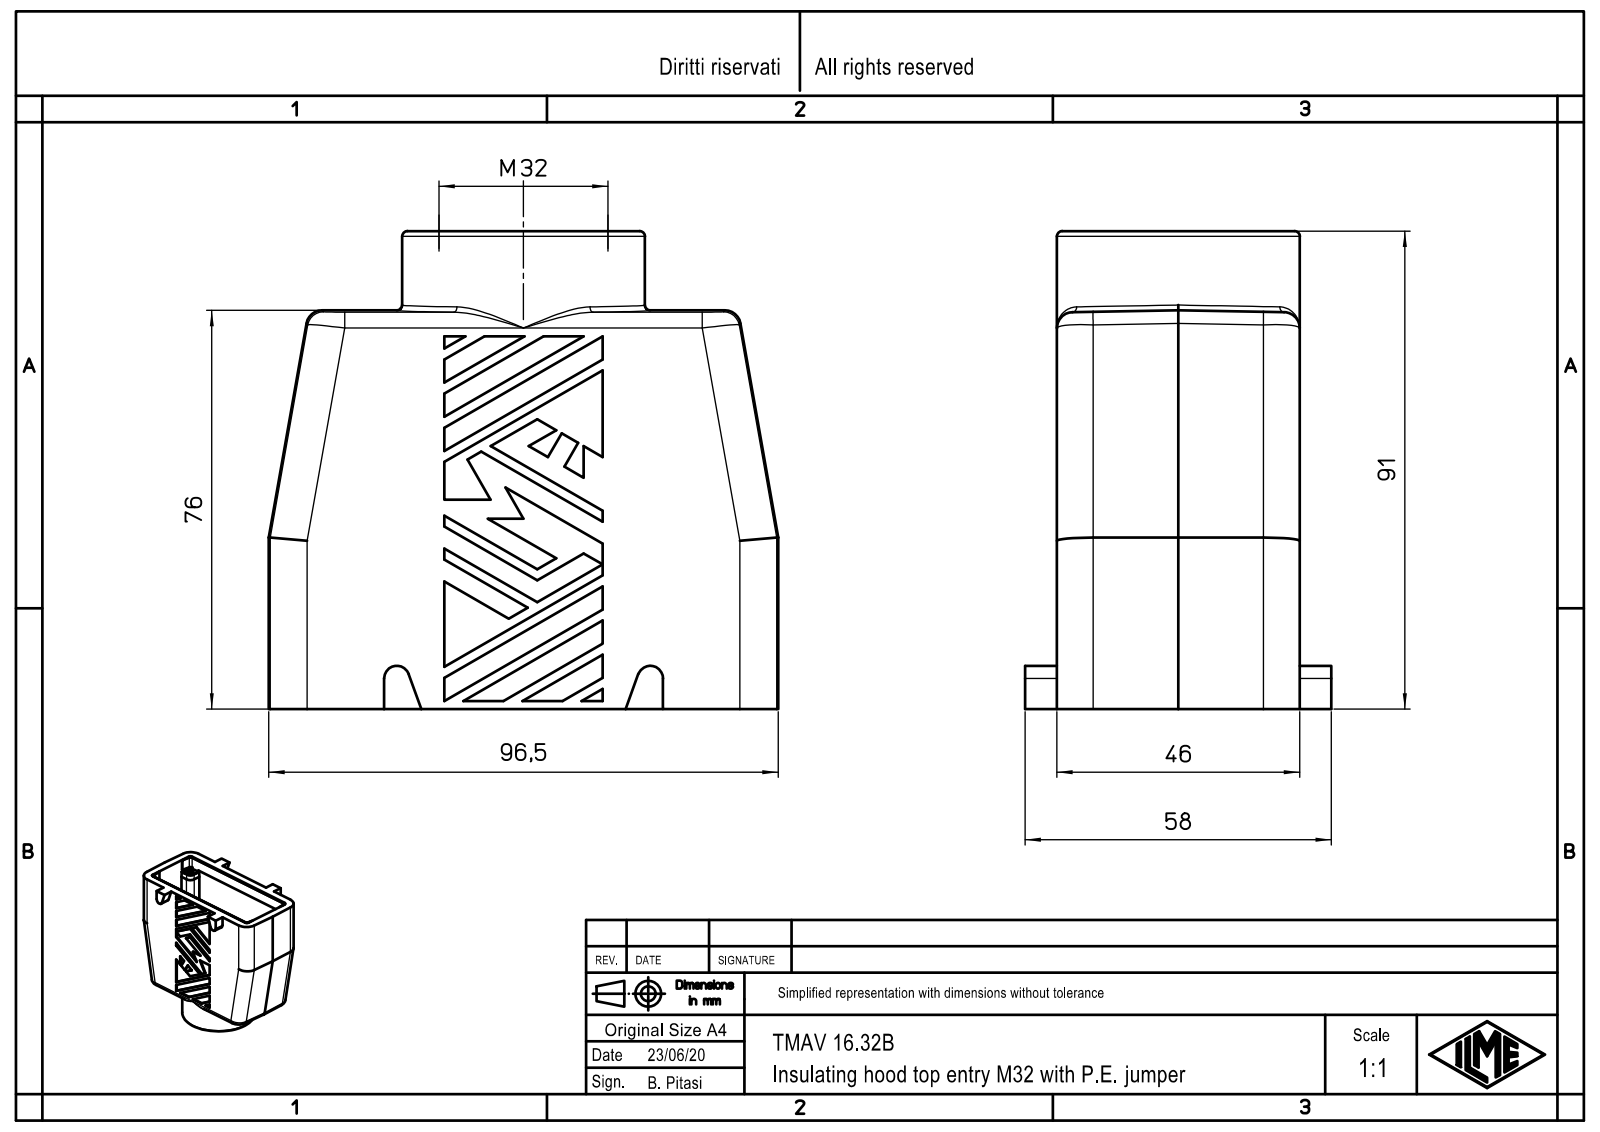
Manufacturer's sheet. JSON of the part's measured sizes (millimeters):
{"part_name": "TMAV_16.32B", "step_written_by": "Creo Elements/Direct Modeling 20.1B 02-Apr-2019 (C) Parametric Technology GmbH (AUTOMOTIVE_DESIGN)", "units": "millimeters", "bodies": {"solids": 1, "faces": 466, "planar": 302, "cylindrical": 82, "other": 82}, "overall_size": [96.5, 90.49, 58], "volume_mm3": 137745, "surface_area_mm2": 51504, "round_holes": [[3, 4], [3.5, 4], [28, 1], [32, 1]], "round_bosses_or_shafts": [[4.8, 4], [46, 1]], "partial_cylinders_radius": [[1.5, 12], [7, 8], [3, 6], [1.3, 4], [1.6, 4], [2, 4], [3.5, 4], [2.4, 2]], "face_to_face_distances": [46, 0.5, 45.5, 69.99, 5.6, 45, 5.3, 5.8, 40.2, 39.7], "hole_center_spacings": [41.03, 27, 77.5, 82.07]}
